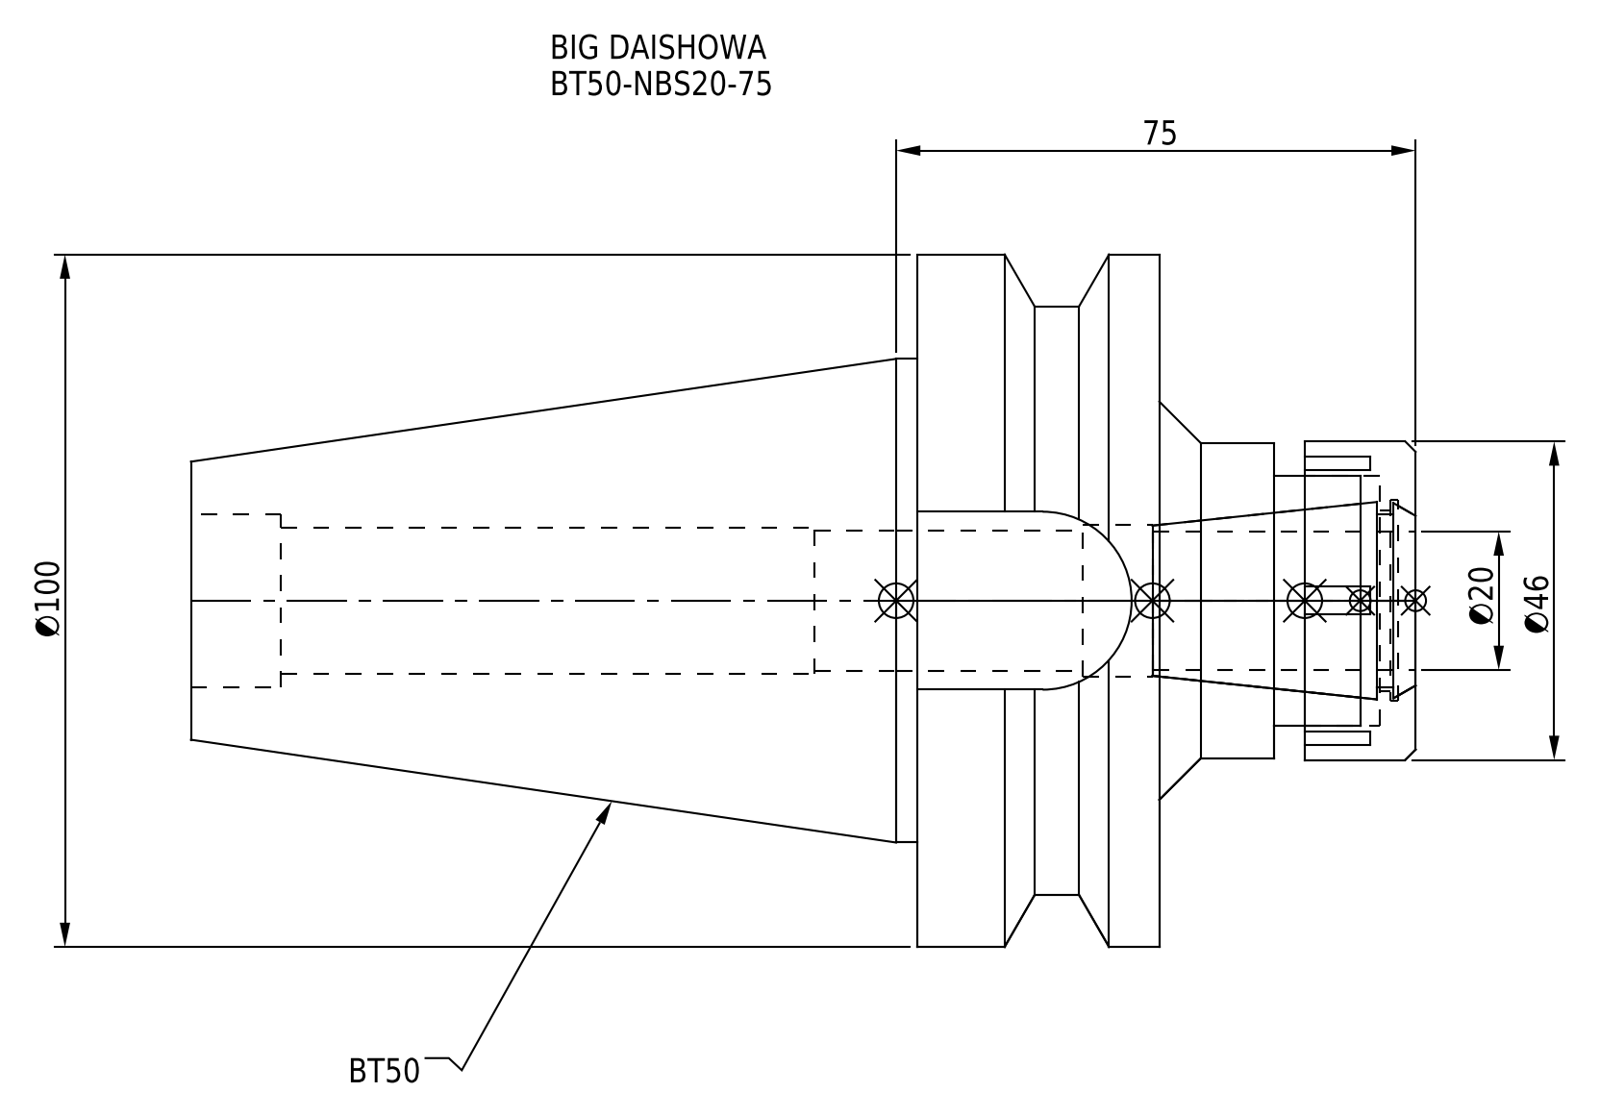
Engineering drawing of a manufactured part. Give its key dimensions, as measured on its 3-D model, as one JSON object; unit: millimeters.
{"part_name": "BT50-NBS20-75-FreeParts; NBN20_1.stp; DXF_TEMP_ASSY_ASM_4_ASM.stp; BT50-NBS20-75_1.stp (+3 more)", "step_written_by": "SolidWorks 2019 (CONFIG_CONTROL_DESIGN)", "units": "millimeters", "bodies": {"solids": 2, "faces": 90, "planar": 44, "cylindrical": 32, "other": 14}, "overall_size": [176.8, 100, 100], "volume_mm3": 483687, "surface_area_mm2": 65975, "round_holes": [[20.3, 1], [21.2, 1], [22, 1], [25, 1], [26, 1], [29, 1], [36, 1]], "round_bosses_or_shafts": [[100, 1], [85, 1], [69.85, 1], [46, 1], [45.5, 1]], "partial_cylinders_radius": [[12.85, 1]], "face_to_face_distances": [35, 37, 72, 8, 176.8, 139.8, 104.8, 70.8, 20.5, 16.5]}
